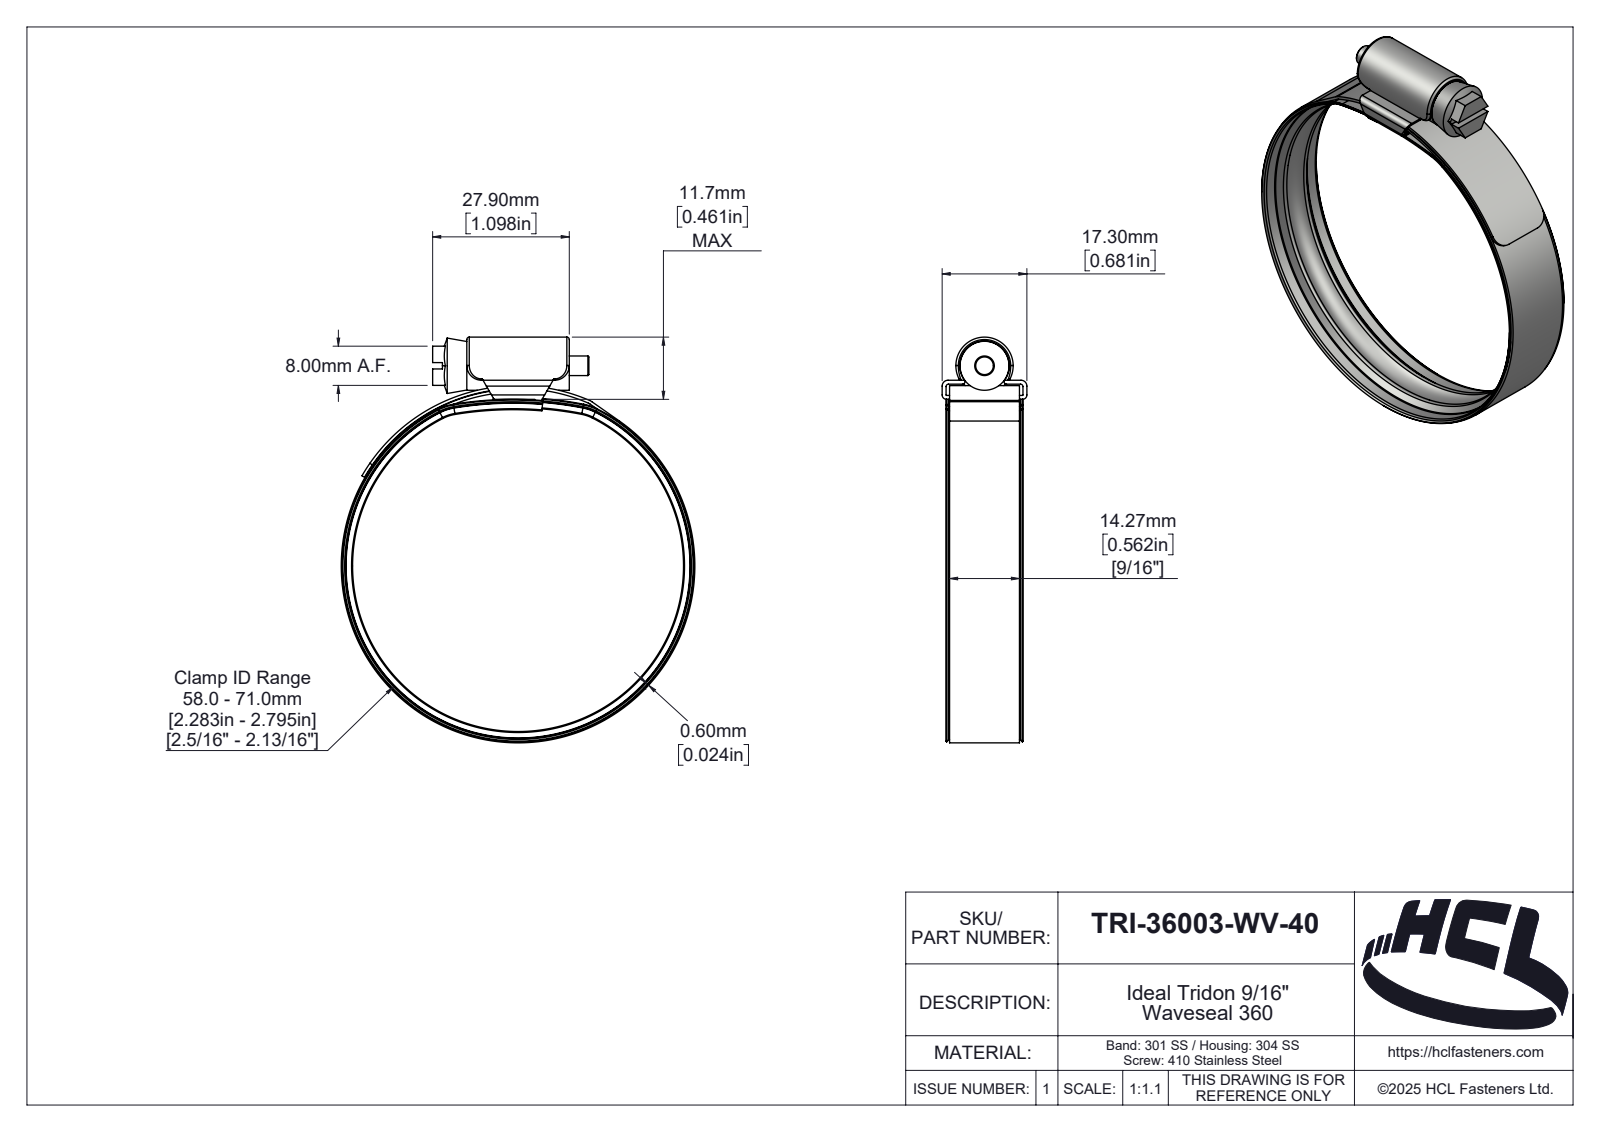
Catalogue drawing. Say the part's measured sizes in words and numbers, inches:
The part is named "TRI-36003-WV-40". Its 3-D file was written by "SolidWorks 2025 (AUTOMOTIVE_DESIGN)". It is 4 solids with 418 faces: 42 planar, 119 cylindrical and 257 other. Overall it measures 3.26 by 2.843 by 0.681 inches. Its volume is 0.361 cubic inches and its surface area 29.16 square inches. Round holes: 1 of diameter 2.772, 1 of diameter 2.795. Round bosses or shafts: 1 of diameter 2.843, 1 of diameter 2.787, 1 of diameter 0.394, 1 of diameter 0.157. Partial cylindrical surfaces (rounded edges, fillets, slot ends): 6 of radius 0.02, 4 of radius 0.118, 2 of radius 0.004, 2 of radius 0.035, 2 of radius 0.047, 2 of radius 0.39, 2 of radius 0.398, 1 of radius 0.018. The main face-to-face distances are 0.031, 0.122, 0.561, 0.024, 0.091, 0.154, 1.098, 0.06, 0.621, 0.65.
